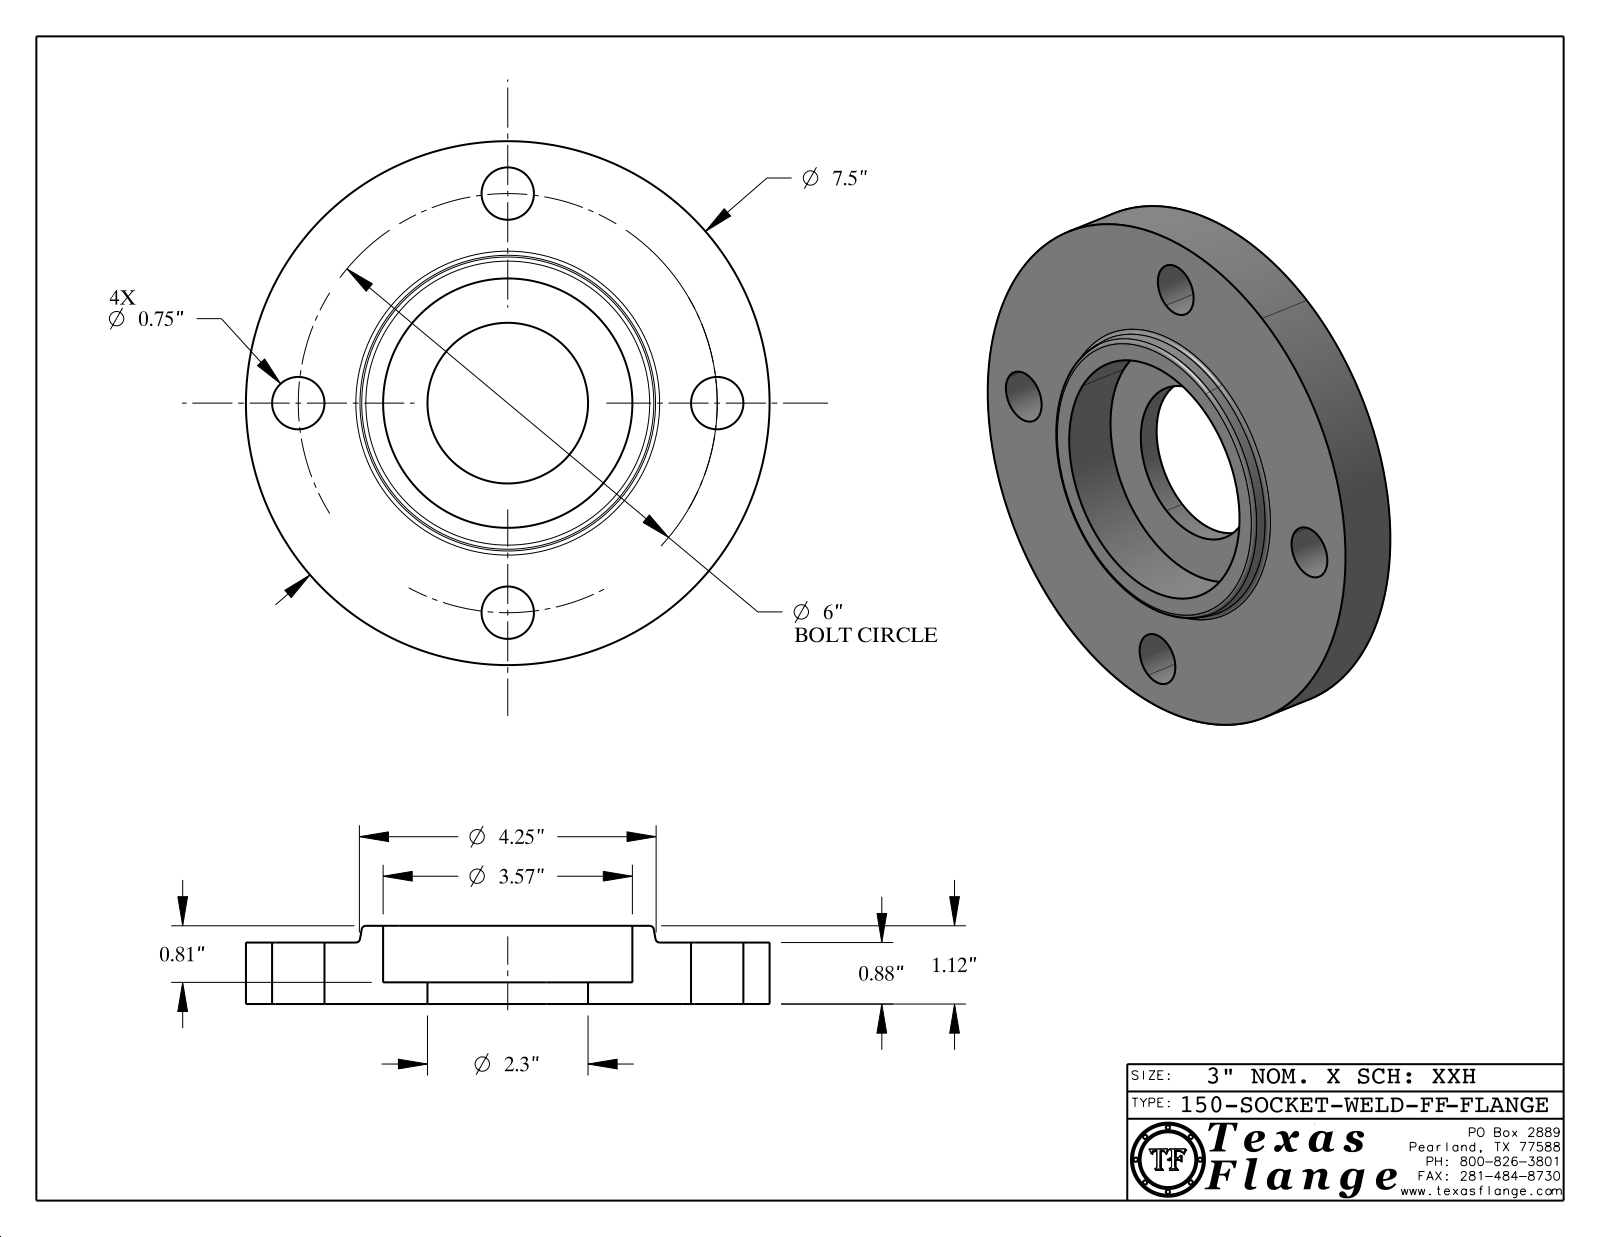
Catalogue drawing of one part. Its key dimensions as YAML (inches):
part_name: "150-SOCKET-WELD-FF"
step_written_by: "CATIA V5 STEP AP214 (AUTOMOTIVE_DESIGN)"
units: inches
bodies: {solids: 1, faces: 410, planar: 370, cylindrical: 34, other: 6}
overall_size: [7.5, 7.5, 1.12]
volume: 31.26
surface_area: 119.2
round_holes:
  - {diameter: 0.75, count: 4}
  - {diameter: 0.495, count: 1}
  - {diameter: 2.3, count: 1}
  - {diameter: 3.57, count: 1}
round_bosses_or_shafts:
  - {diameter: 0.03, count: 8}
  - {diameter: 7.5, count: 1}
  - {diameter: 0.39, count: 1}
face_to_face_distances: [0.88, 0.31, 0.57, 1.12, 0.81, 0.24, 0.865, 0.555, 0.015, 0.255]
hole_center_spacings: [3, 4.243, 2.296, 5.543, 6]
